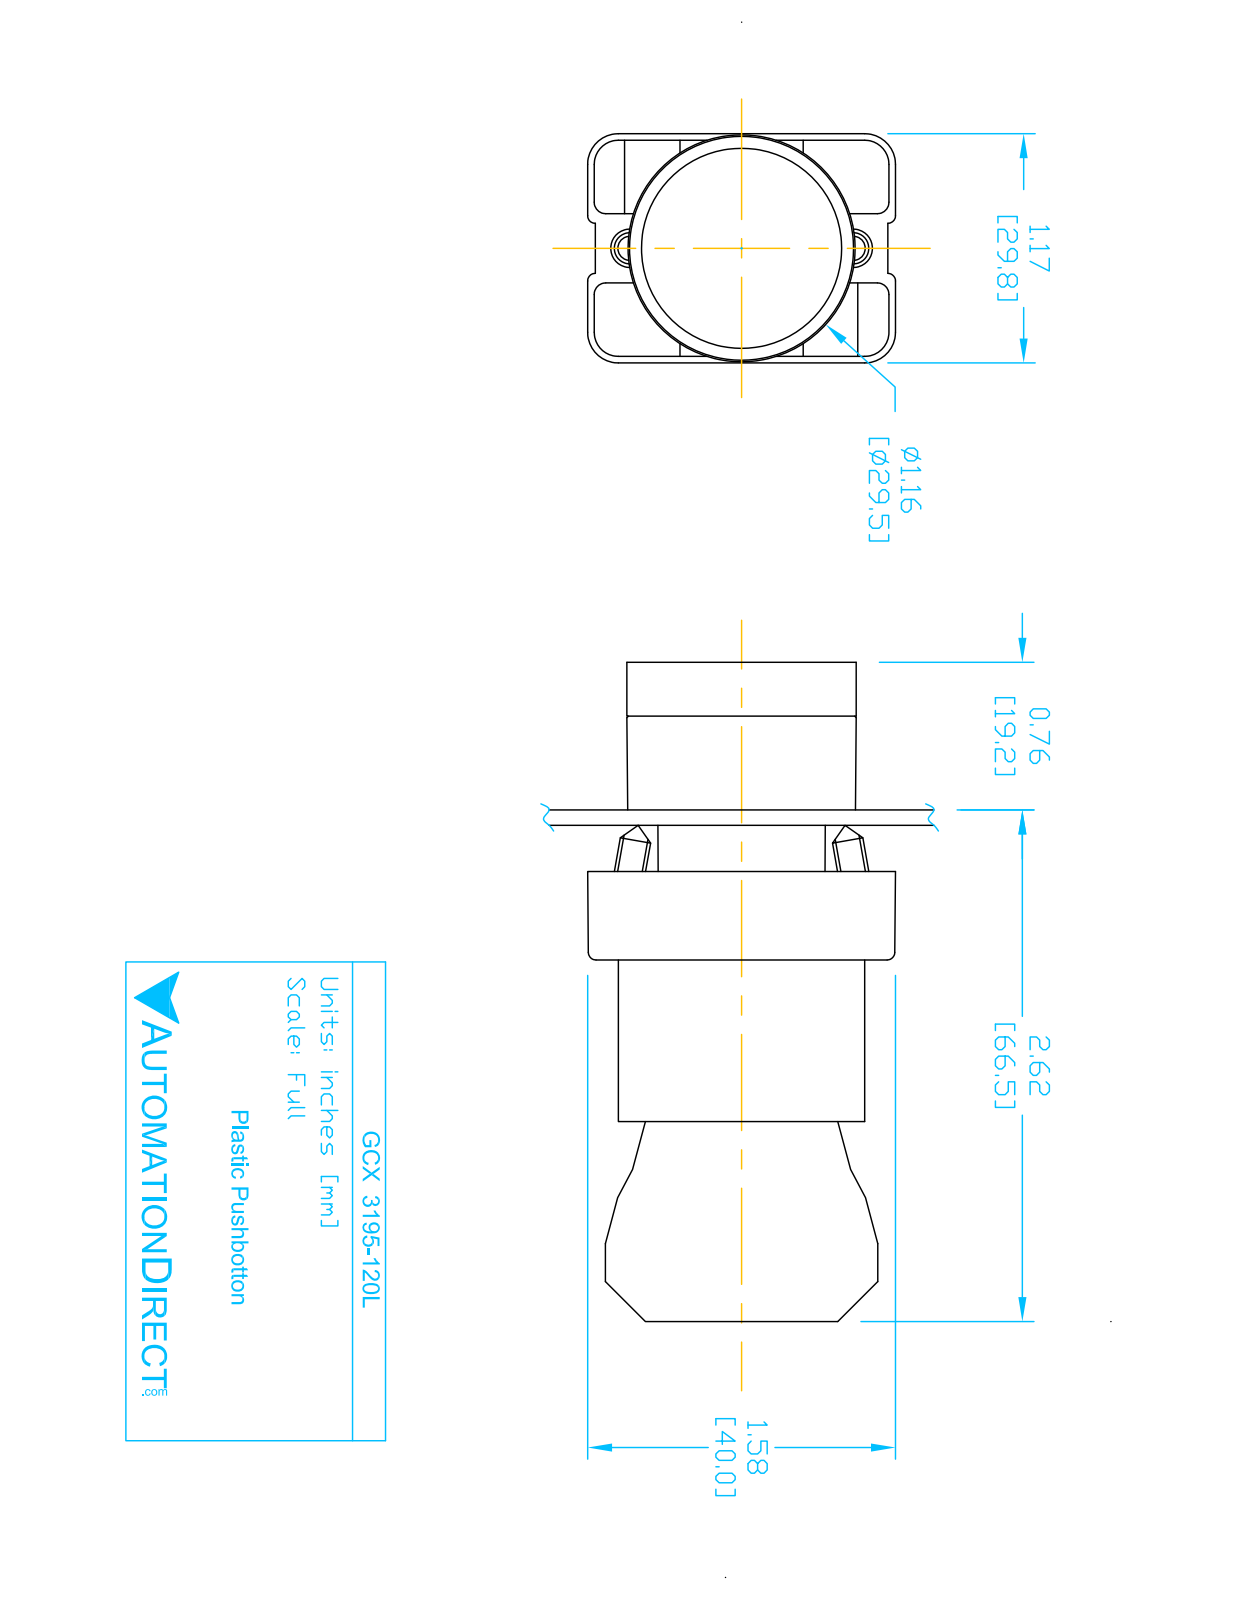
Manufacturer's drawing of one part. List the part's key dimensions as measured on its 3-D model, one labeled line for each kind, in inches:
Part name (STEP PRODUCT): ECX3029-2; GCX3195-120L; GCX3195L OPERATOR; ECX1050 (+1 more)
STEP written by: SolidWorks 2016 (AUTOMOTIVE_DESIGN)
Units: inches
Bodies: 8 solids, 431 faces (252 planar, 148 cylindrical, 31 other)
Overall size (bounding box): 3.319 × 1.581 × 1.177
Volume: 2.794 in³ · Surface area: 38.77 in²
Round holes (diameter × count): ⌀0.079 ×2, ⌀0.124 ×2, ⌀0.13 ×2, ⌀0.087 ×1, ⌀0.197 ×1, ⌀0.469 ×1, ⌀0.878 ×1, ⌀0.888 ×1, ⌀1.024 ×1
Round bosses / shafts (diameter × count): ⌀0.157 ×4, ⌀1.175 ×1, ⌀1.004 ×1, ⌀0.945 ×1, ⌀0.856 ×1, ⌀0.78 ×1, ⌀0.504 ×1
Partial cylindrical surfaces — rounded edges, fillets, slot ends (radius × count): R0.059 ×24, R0.041 ×12, R0.124 ×12, R0.157 ×12, R0.039 ×8, R0.128 ×2, R0.02 ×1, R0.063 ×1
Main face-to-face distances: 0.827, 0.579, 2.02, 1.193, 1.171, 0.276, 2.295, 1.469, 0.031, 0.033
Hole centre spacings: 0.236, 0.544, 0.472, 0.49
